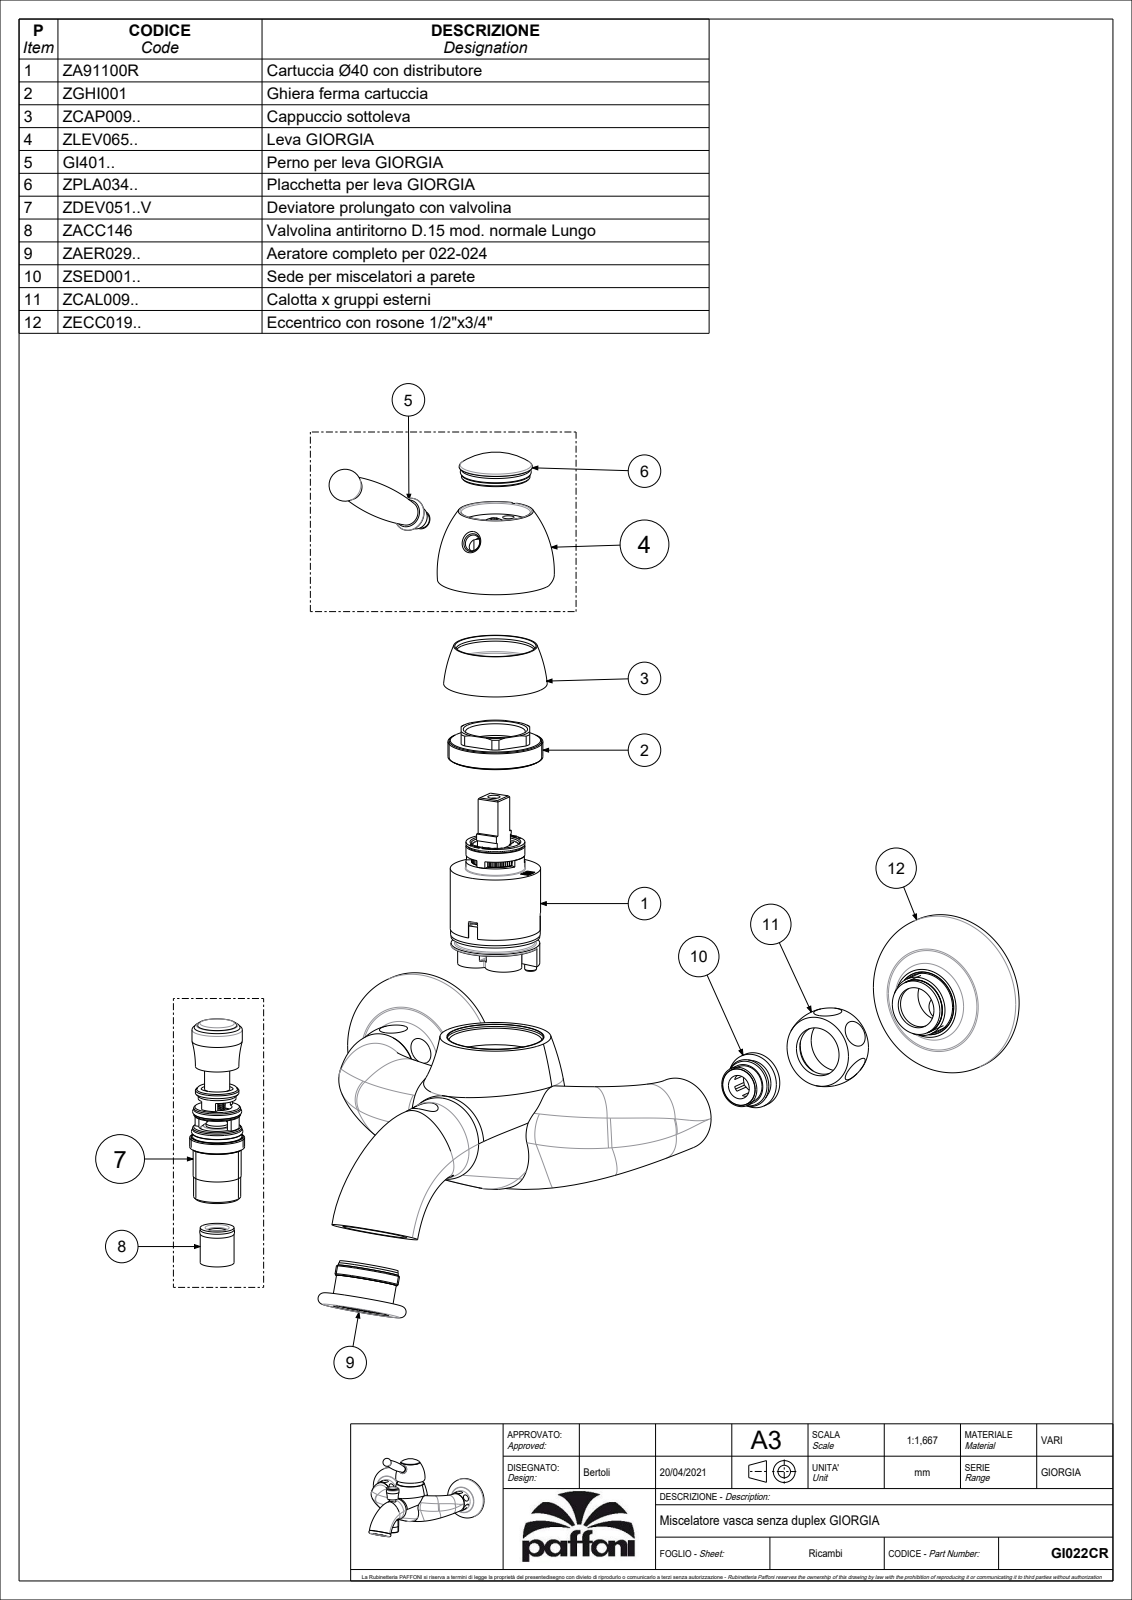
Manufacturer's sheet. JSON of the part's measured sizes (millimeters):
{"part_name": "GI022CR", "step_written_by": "CREO PARAMETRIC BY PTC INC, 2020044 (CONFIG_CONTROL_DESIGN)", "units": "millimeters", "bodies": {"solids": 4, "faces": 2364, "planar": 1301, "cylindrical": 645, "other": 418}, "overall_size": [220, 195.33, 138.76], "volume_mm3": 400613, "surface_area_mm2": 143751, "round_holes": [[0.5, 91], [5, 4], [8, 4], [12, 3], [18, 3], [3.3, 2], [6.27, 2], [10.5, 2], [11, 2], [21.5, 2], [24.1, 2], [25, 2]], "round_bosses_or_shafts": [[24, 4], [70, 2], [28.14, 2], [15.9, 2], [9.4, 2], [39.5, 1], [39.2, 1], [38.8, 1]], "partial_cylinders_radius": [[0.5, 63], [0.2, 24], [0.3, 8], [1.5, 4], [5.5, 2], [7.5, 2], [2, 1], [3.5, 1]], "face_to_face_distances": [1, 3, 32, 18.5, 6, 6.5, 39.5, 7, 17.5, 11.5], "hole_center_spacings": [3.82, 5.73, 1.91, 7.64, 1.99, 5.05, 5.72, 9.55]}
